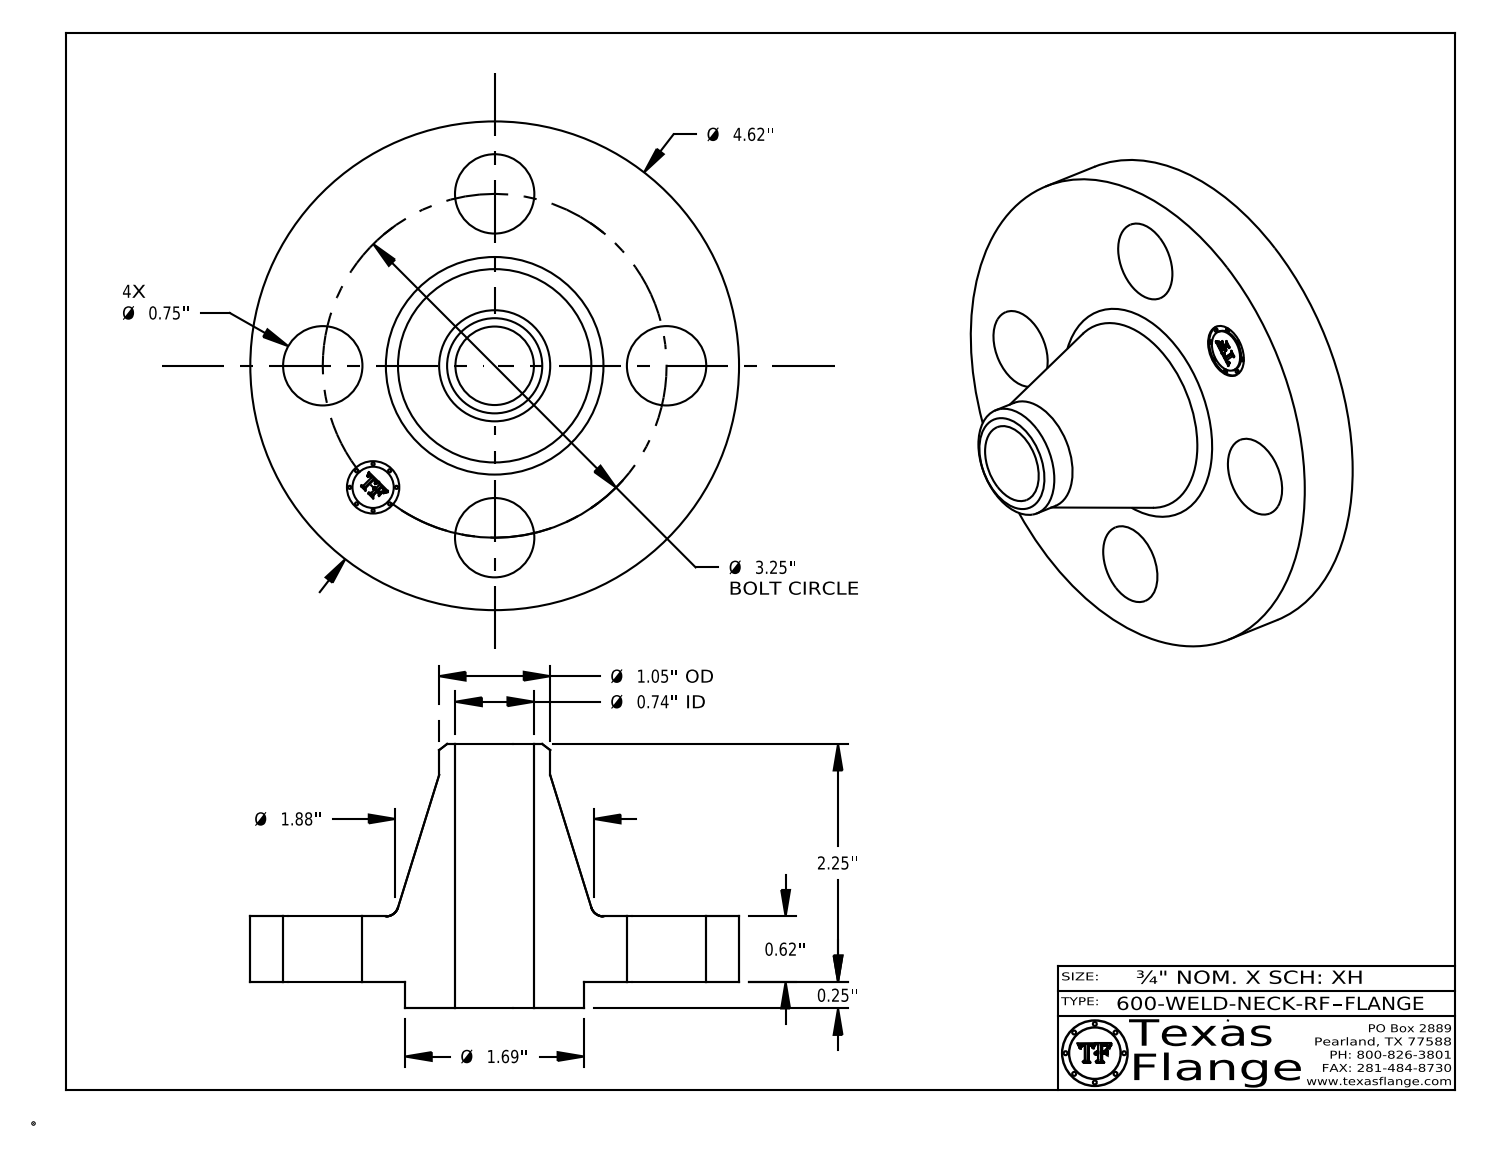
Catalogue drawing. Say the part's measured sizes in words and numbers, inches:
The part is named "600-WELD-NECK-RF". Its 3-D file was written by "CATIA V5 STEP AP214 (AUTOMOTIVE_DESIGN)". It is 1 solid with 411 faces: 369 planar, 36 cylindrical and 6 other. Overall it measures 4.62 by 4.62 by 2.5 inches. Its volume is 11.35 cubic inches and its surface area 56.45 square inches. Round holes: 4 of diameter 0.75, 1 of diameter 0.495, 1 of diameter 0.742. Round bosses or shafts: 8 of diameter 0.03, 1 of diameter 4.62, 1 of diameter 1.69, 1 of diameter 1.05, 1 of diameter 0.39. The main face-to-face distances are 0.62, 0.25, 0.87, 2.5, 2.25, 1.63, 0.855, 0.605, 0.015, 1.645. The hole center spacings are 1.625, 2.298, 1.244, 3.003, 3.25.
